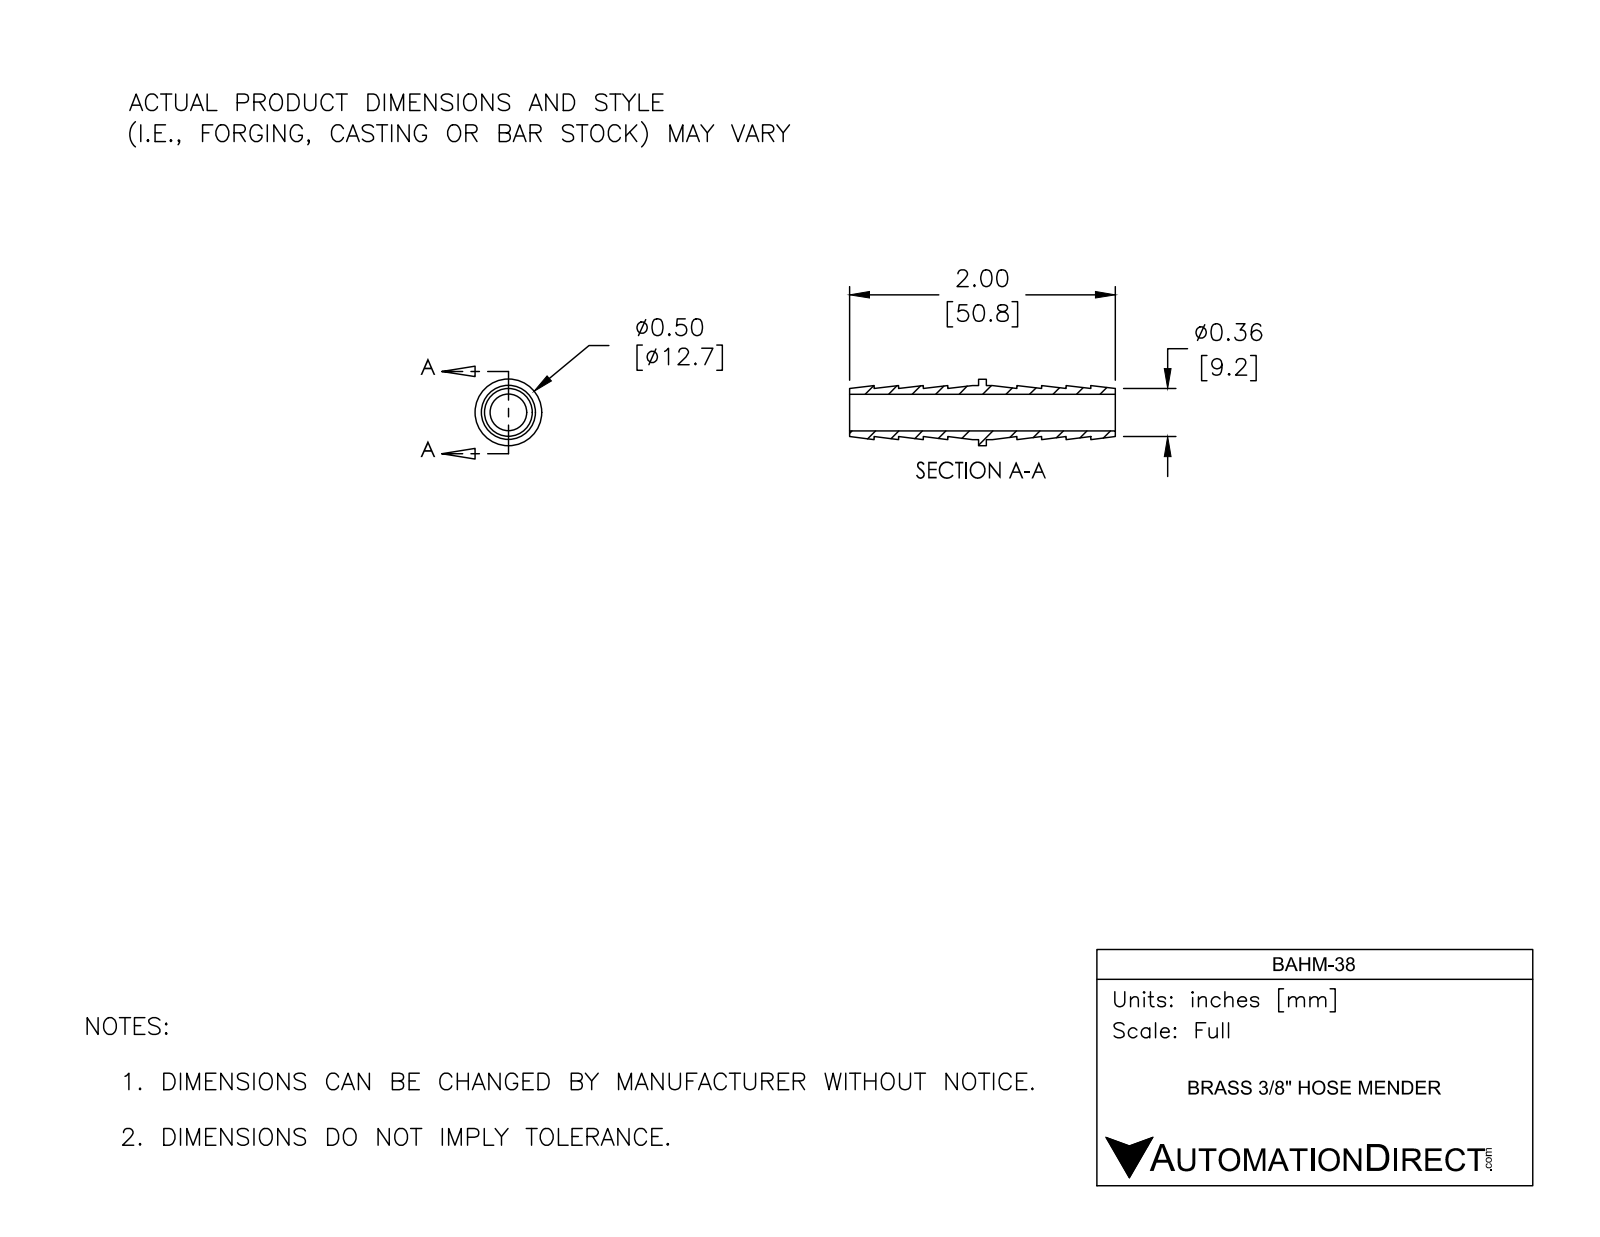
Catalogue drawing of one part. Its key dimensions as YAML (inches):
part_name: "BAHM-38"
step_written_by: "SolidWorks 2017 (AUTOMOTIVE_DESIGN)"
units: inches
bodies: {solids: 1, faces: 40, planar: 12, cylindrical: 8, other: 20}
overall_size: [2, 0.5, 0.5]
volume: 0.119
surface_area: 4.639
round_holes:
  - {diameter: 0.276, count: 1}
round_bosses_or_shafts:
  - {diameter: 0.5, count: 1}
  - {diameter: 0.408, count: 1}
face_to_face_distances: [0.185, 0.37, 1.26, 0.555, 1.445, 1.075, 1.63, 0.89, 0.97, 1.03]
